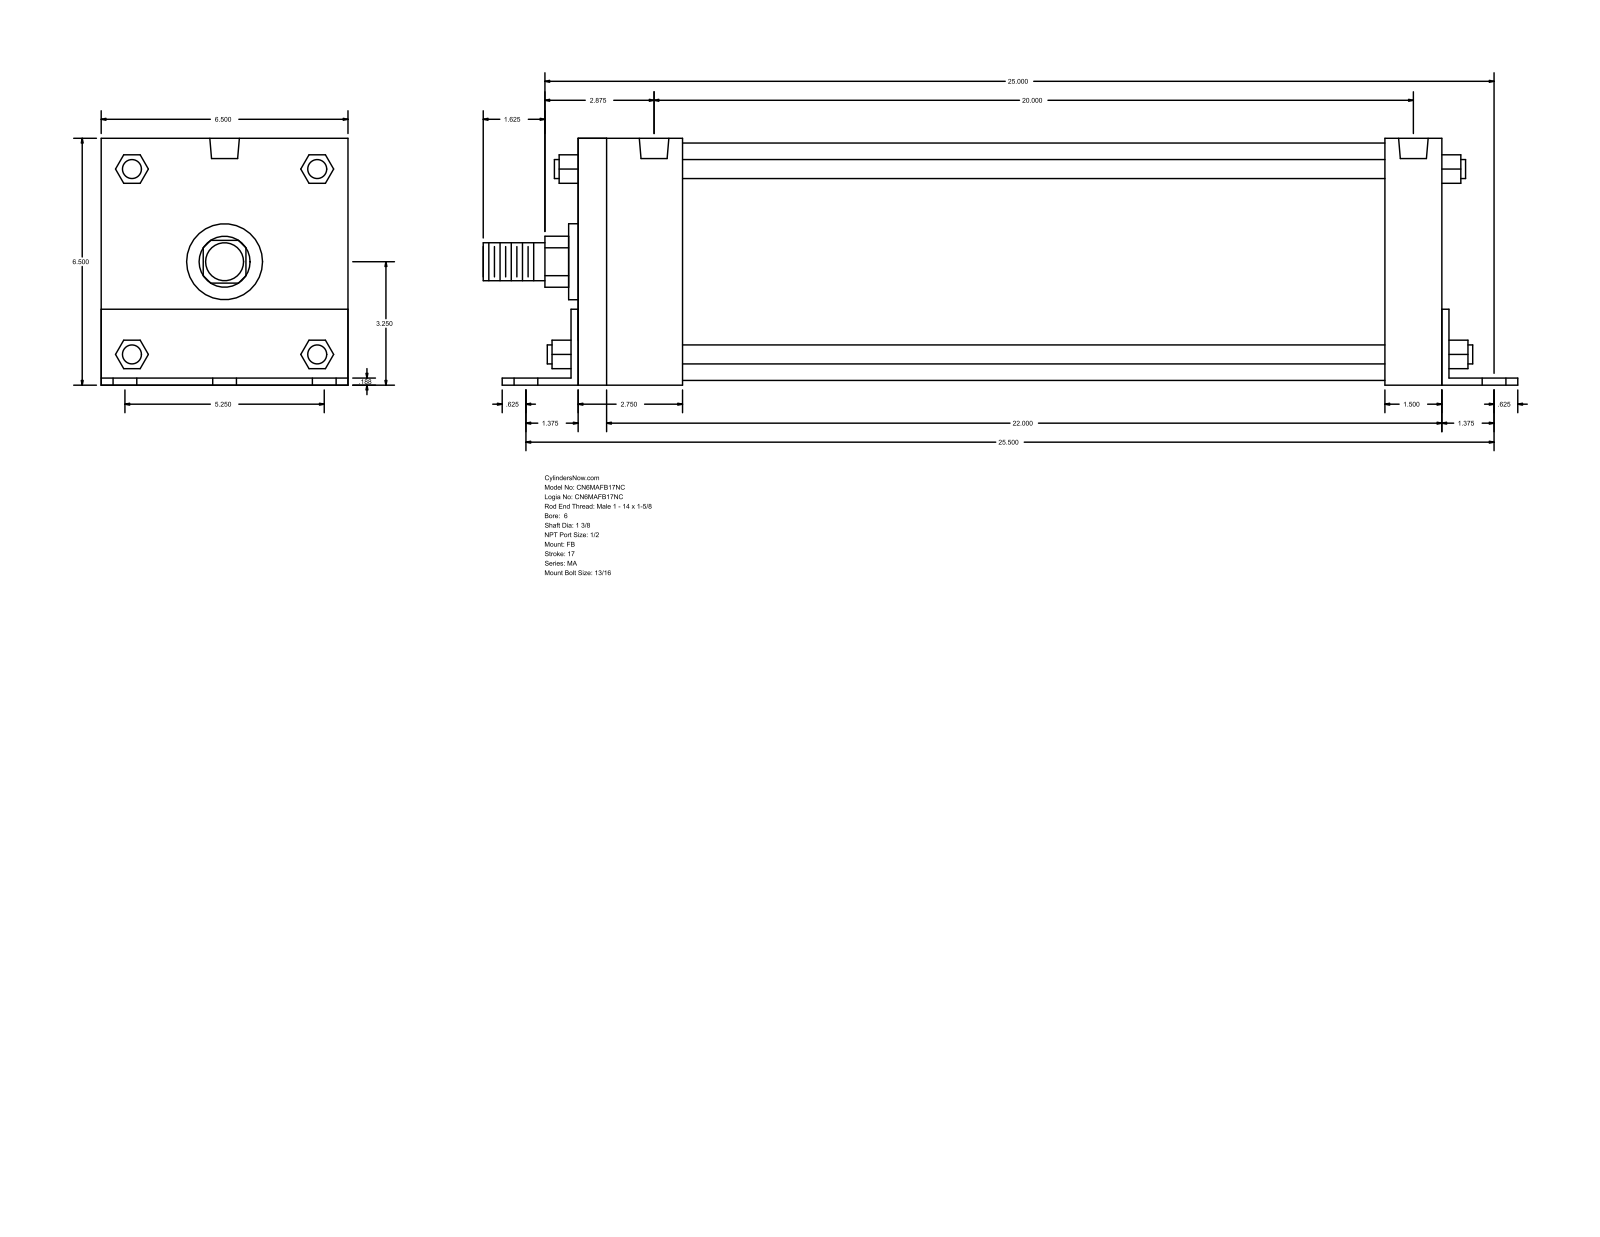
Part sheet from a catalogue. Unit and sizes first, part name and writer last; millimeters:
Units: millimetres
Overall size (bounding box): 688.98 × 165.15 × 165.1
Round holes (diameter × count): ⌀20.64 ×6, ⌀17.46 ×4, ⌀19.77 ×2
Round bosses / shafts (diameter × count): ⌀12.7 ×4, ⌀158.75 ×1, ⌀50.8 ×1, ⌀34.92 ×1, ⌀25.4 ×1
Partial cylindrical surfaces — rounded edges, fillets, slot ends (radius × count): R17.06 ×1, R32.05 ×1
Main face-to-face distances: 165.1, 4.76, 574.67, 165.15, 4.71, 160.39, 4.77, 38.1, 42.86, 584.2
Hole centre spacings: 66.67, 647.97, 644.53, 83.82, 85.78, 108.6, 133.34, 504.82
Bodies: 0 solids, 140 faces (105 planar, 35 cylindrical, 0 other)
Part name (STEP PRODUCT): MA_FB__0600_1.375
STEP written by: GSSL Pune (CONFIG_CONTROL_DESIGN)
